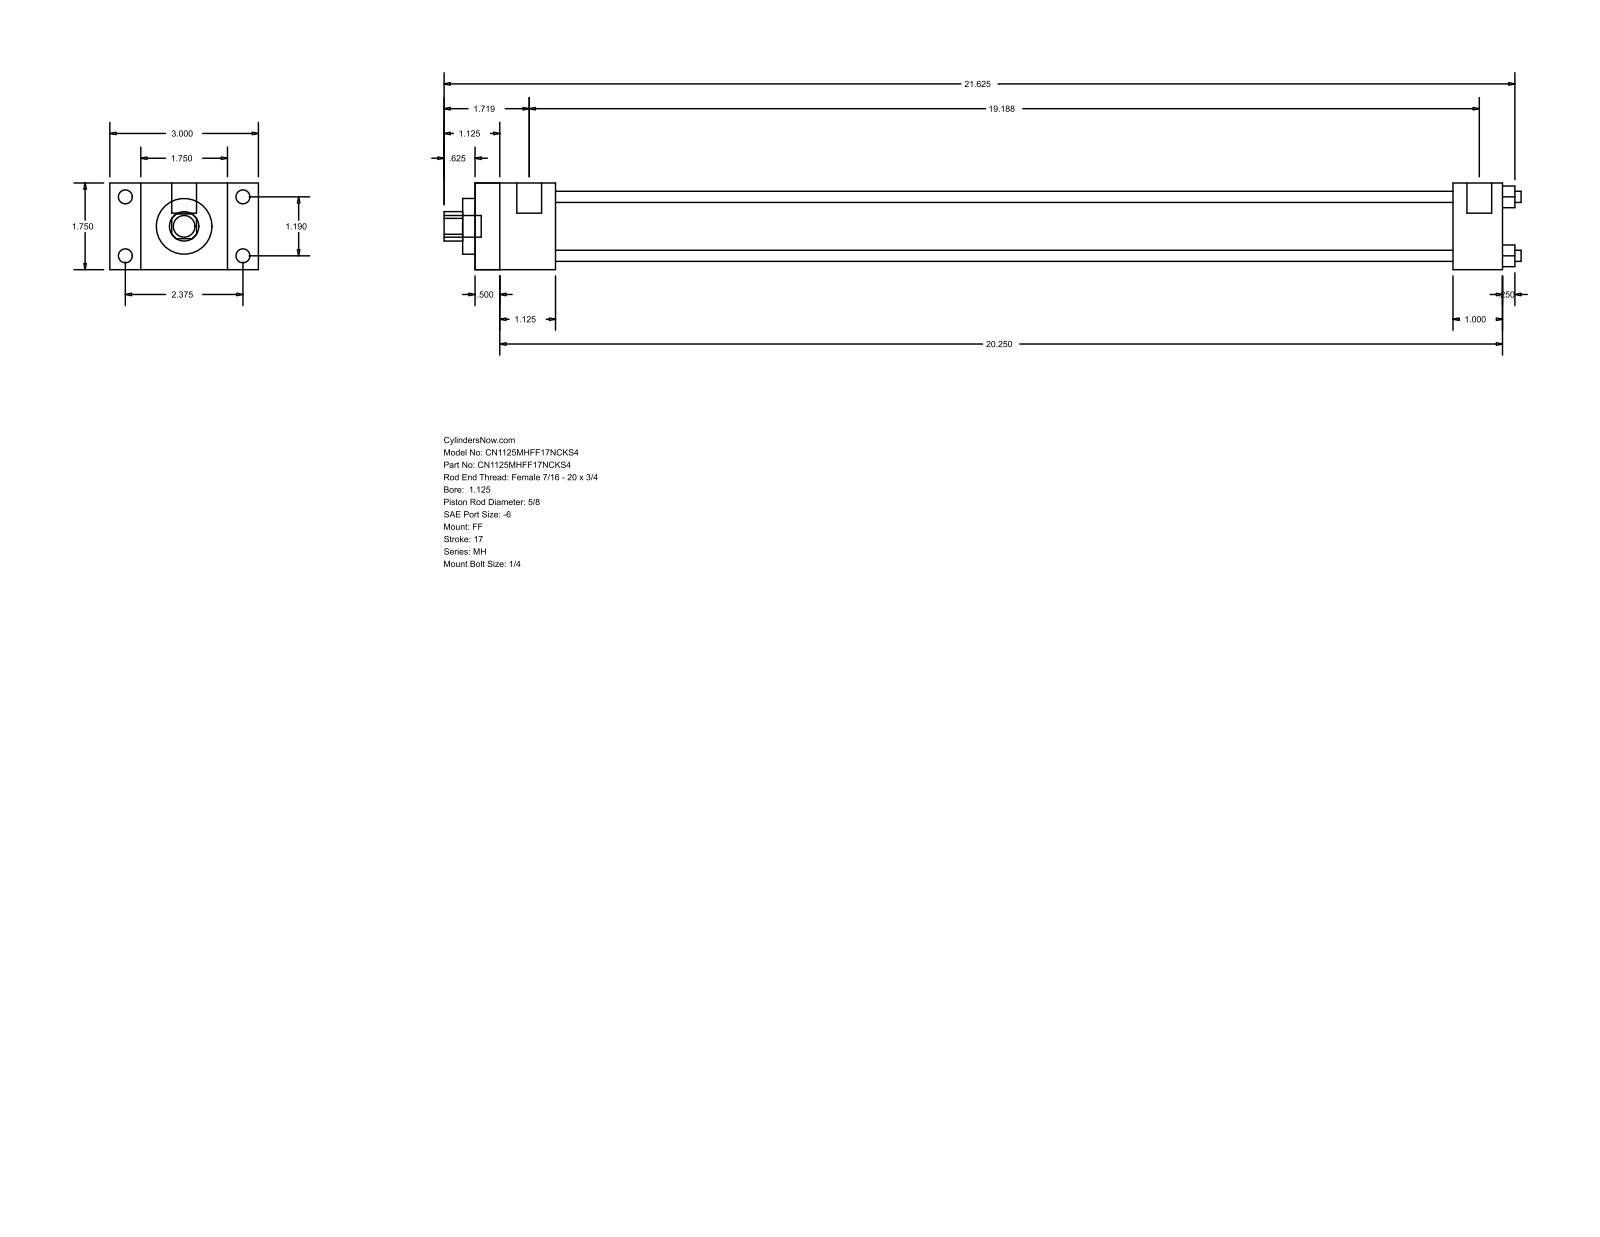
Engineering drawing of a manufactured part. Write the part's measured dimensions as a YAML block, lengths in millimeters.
part_name: "MH_FF__0112_0.625"
step_written_by: "GSSL Pune (CONFIG_CONTROL_DESIGN)"
units: millimeters
bodies: {solids: 0, faces: 92, planar: 64, cylindrical: 28, other: 0}
overall_size: [552.45, 76.2, 44.45]
round_holes:
  - {diameter: 5.71, count: 4}
  - {diameter: 15.88, count: 1}
  - {diameter: 28.57, count: 1}
  - {diameter: 34.92, count: 1}
round_bosses_or_shafts:
  - {diameter: 7.14, count: 4}
  - {diameter: 5.56, count: 4}
  - {diameter: 12.7, count: 2}
  - {diameter: 11.11, count: 1}
partial_cylinders:
  - {radius: 7.54, count: 1}
face_to_face_distances: [44.46, 527.04, 15.87, 12.69, 514.35, 60.33, 28.58, 41.27, 501.64, 488.95]
hole_center_spacings: [21.37, 30.22, 42.74]
